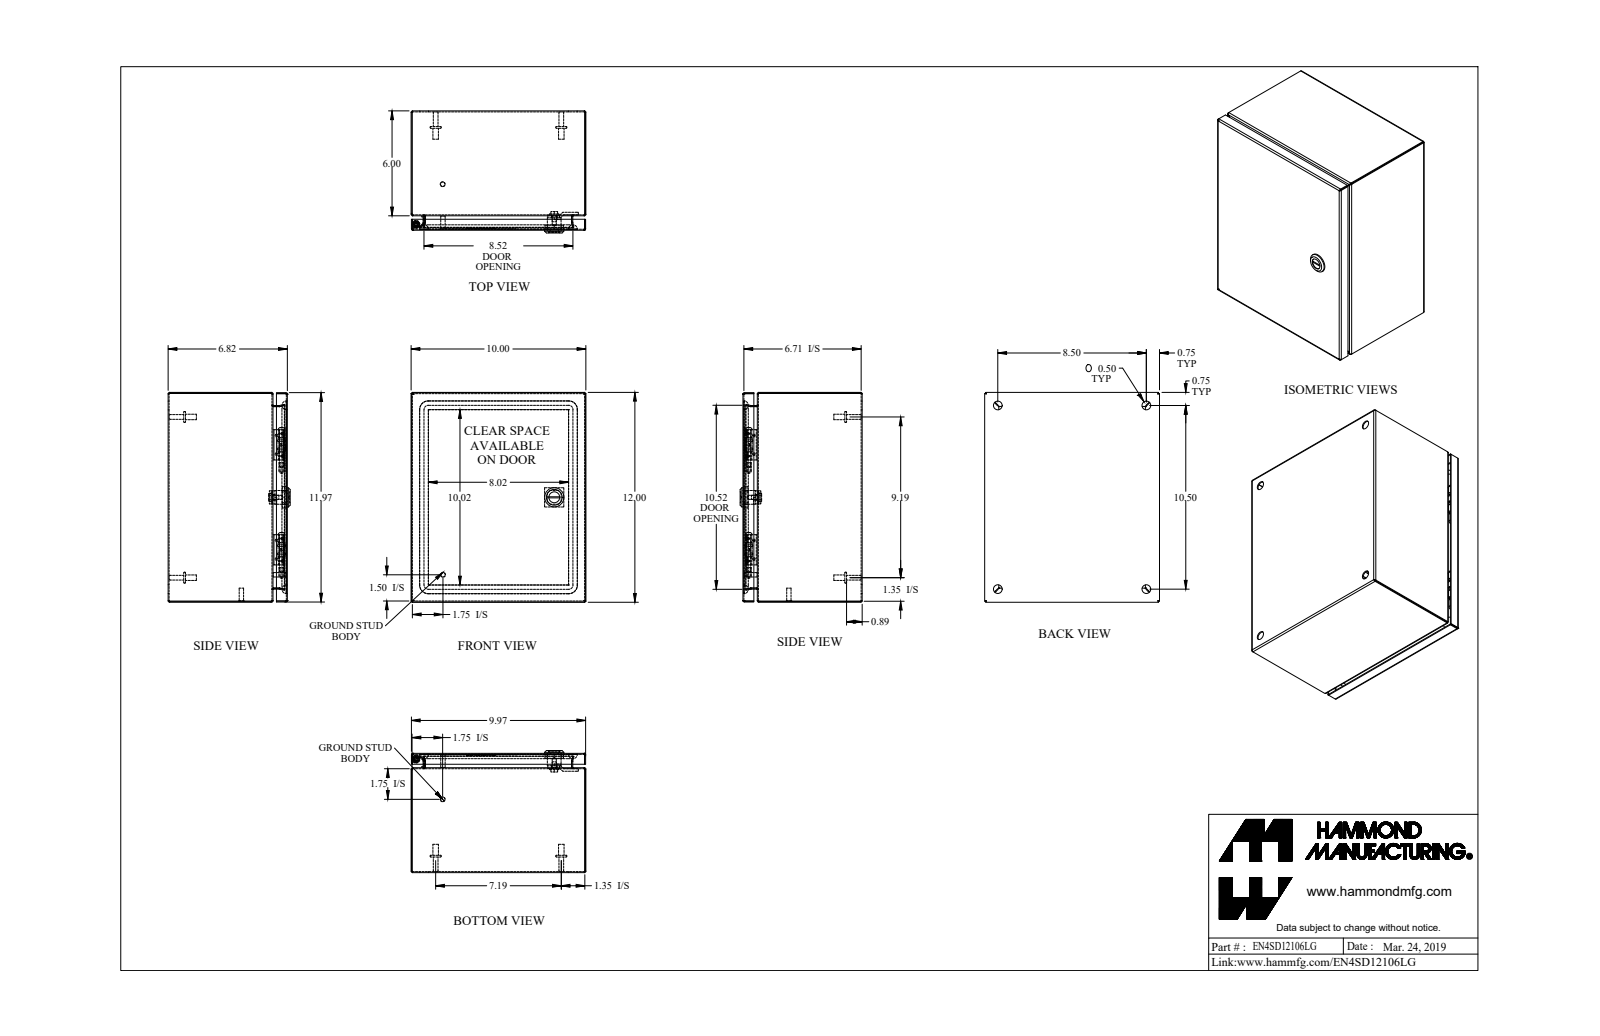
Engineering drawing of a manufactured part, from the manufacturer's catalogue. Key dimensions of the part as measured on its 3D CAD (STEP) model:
Part name (STEP PRODUCT): EN4SD12106LG_Default
STEP written by: SolidWorks 2019 (CONFIG_CONTROL_DESIGN)
Units: inches
Bodies: 21 solids, 634 faces (285 planar, 213 cylindrical, 136 other)
Overall size (bounding box): 12 × 10 × 6.982
Volume: 38.3 in³ · Surface area: 1 281 in²
Round holes (diameter × count): ⌀0.5 ×4, ⌀0.172 ×1, ⌀0.232 ×1, ⌀0.24 ×1, ⌀0.242 ×1, ⌀0.625 ×1, ⌀0.785 ×1
Round bosses / shafts (diameter × count): ⌀0.625 ×4, ⌀0.313 ×4, ⌀0.27 ×4, ⌀0.281 ×2, ⌀0.25 ×2, ⌀1.1 ×1, ⌀0.525 ×1, ⌀0.455 ×1
Partial cylindrical surfaces — rounded edges, fillets, slot ends (radius × count): R0.029 ×21, R0.086 ×21, R0.25 ×16, R19 ×8, R0.006 ×4, R0.062 ×4, R0.499 ×4, R0.125 ×2
Main face-to-face distances: 0.057, 6.765, 9.943, 6.708, 6.822, 11.943, 9.886, 10, 11.886, 12
Hole centre spacings: 8.5, 10.5, 13.509, 5.356, 5.356, 9.106, 9.107
